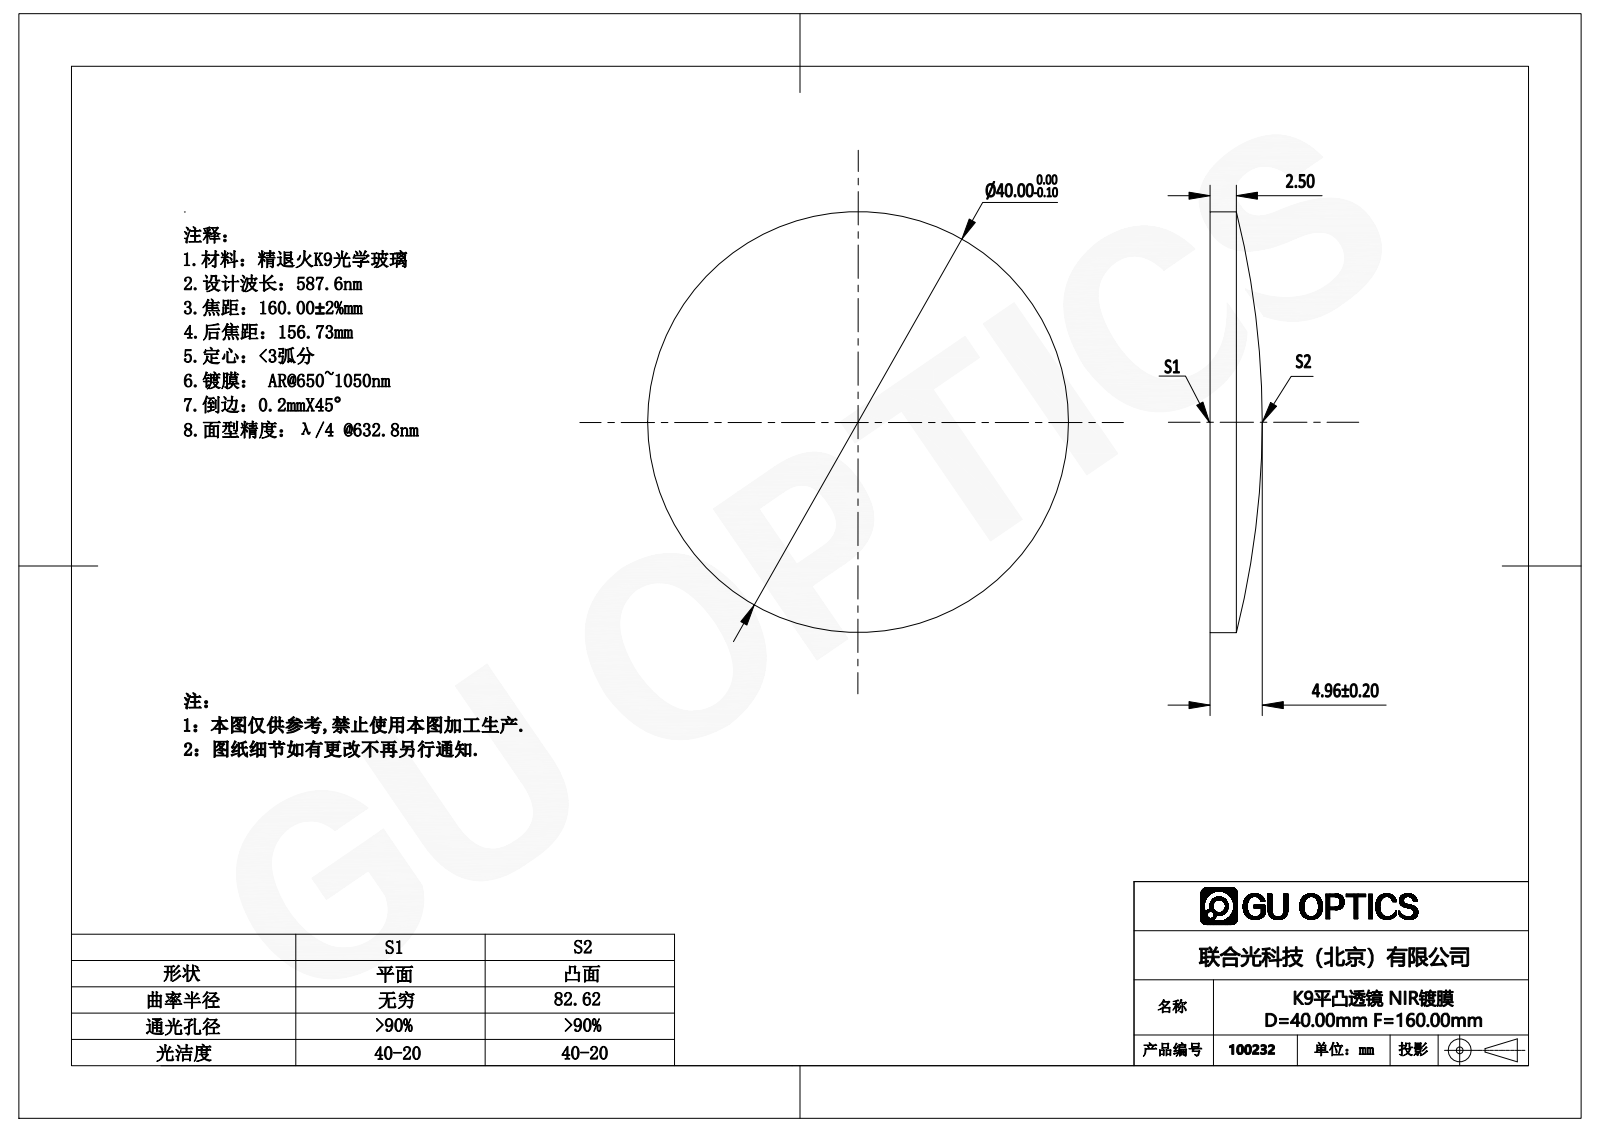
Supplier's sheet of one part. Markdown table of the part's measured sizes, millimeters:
| quantity | value |
| --- | --- |
| part name | 100232 |
| STEP written by | SolidWorks 2016 (AUTOMOTIVE_DESIGN) |
| units | millimeters |
| bodies | 1 solid, 5 faces (1 planar, 2 cylindrical, 2 other) |
| overall size | 40 × 40 × 4.96 |
| volume | 4 695 mm³ |
| surface area | 2 846 mm² |
| round bosses / shafts (diameter × count) | 40 × 1 |
